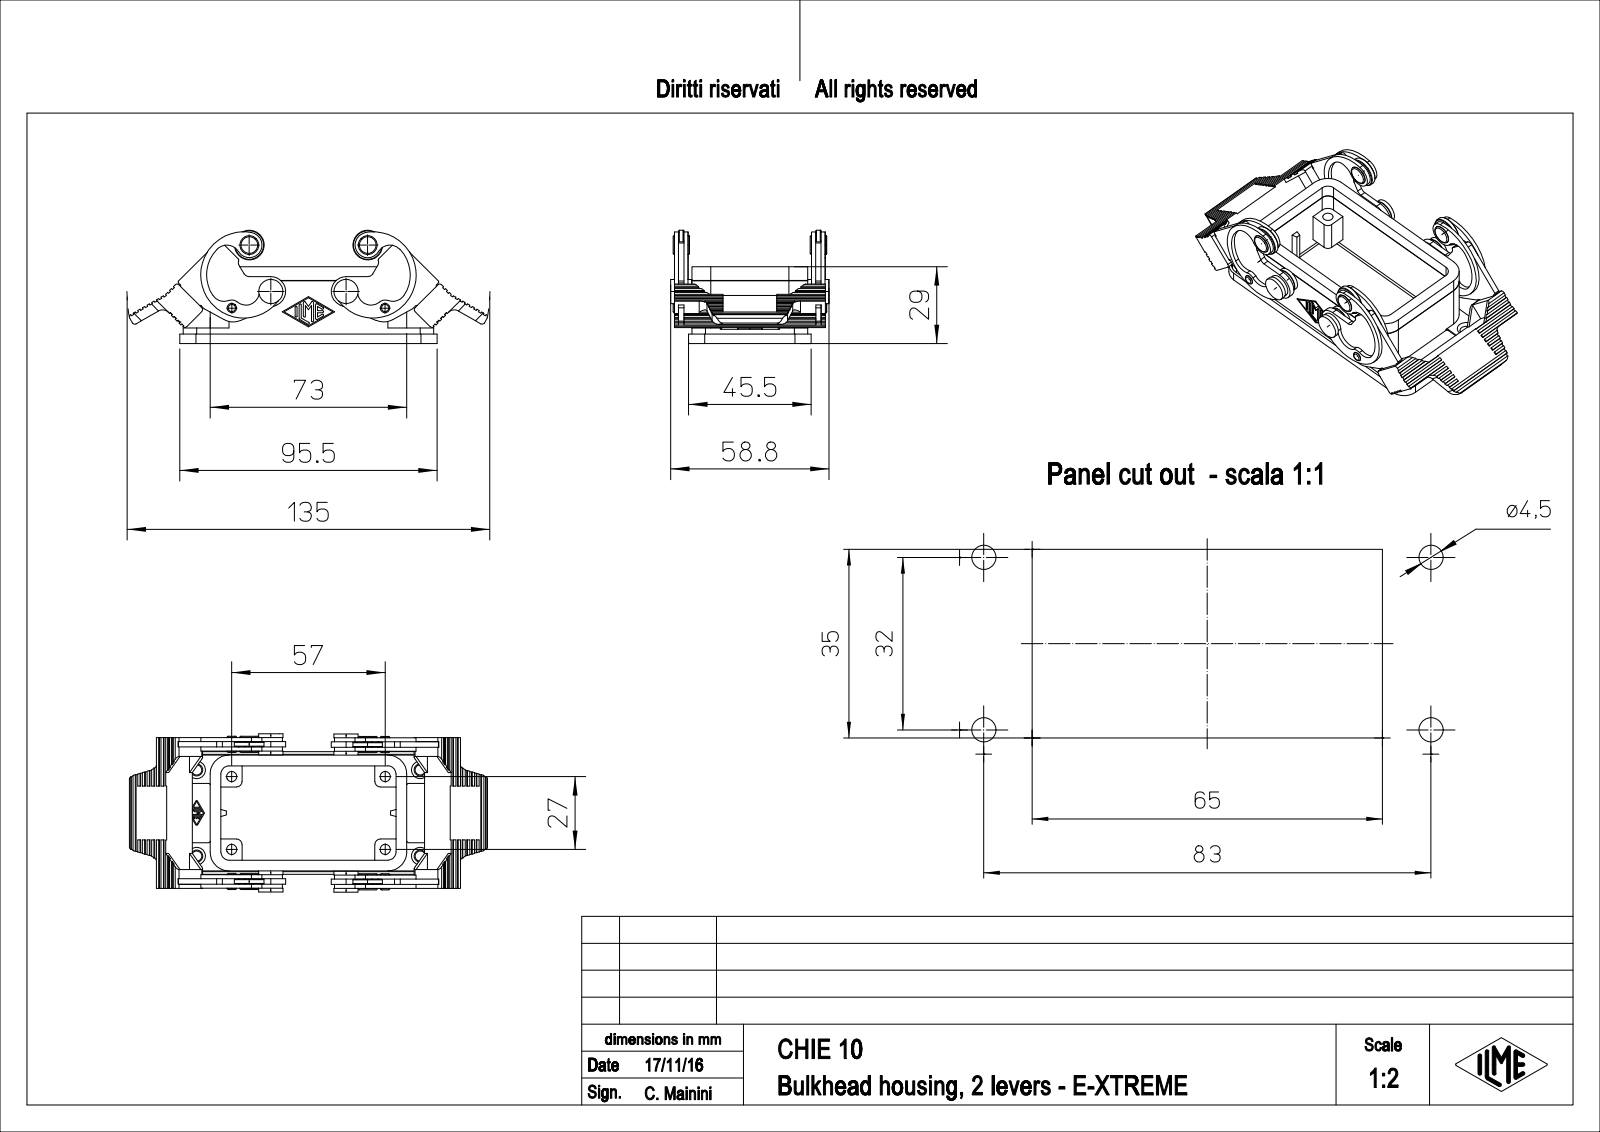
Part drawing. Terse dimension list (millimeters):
name: CHIE_10
written by: PTC Creo Elements/Direct Modeling 19.0E 27-Jun-2016 (C) Parametric Technology GmbH (AUTOMOTIVE_DESIGN)
unit: mm
bodies: 1 solid, 1098 faces (649 planar, 377 cylindrical, 72 other)
size: 132.97 × 58.8 × 42.02
volume: 53 104 mm³; area: 39 728 mm²
holes: 8× ⌀3.8, 4× ⌀4.5, 4× ⌀5, 2× ⌀3.1, 2× ⌀4
bosses: 2× ⌀11, 2× ⌀9, 2× ⌀7, 2× ⌀4.8, 2× ⌀3.5, 2× ⌀3
rounds: 16× R3, 14× R0.38, 14× R5, 12× R0.5, 11× R0.17, 10× R1, 8× R2, 8× R4
face distances: 4, 3.5, 2, 39, 50.9, 1.5, 5, 3, 43, 50.8
hole spacings: 13.24, 32.24, 70.04, 75.96, 19, 24.25, 27, 32
